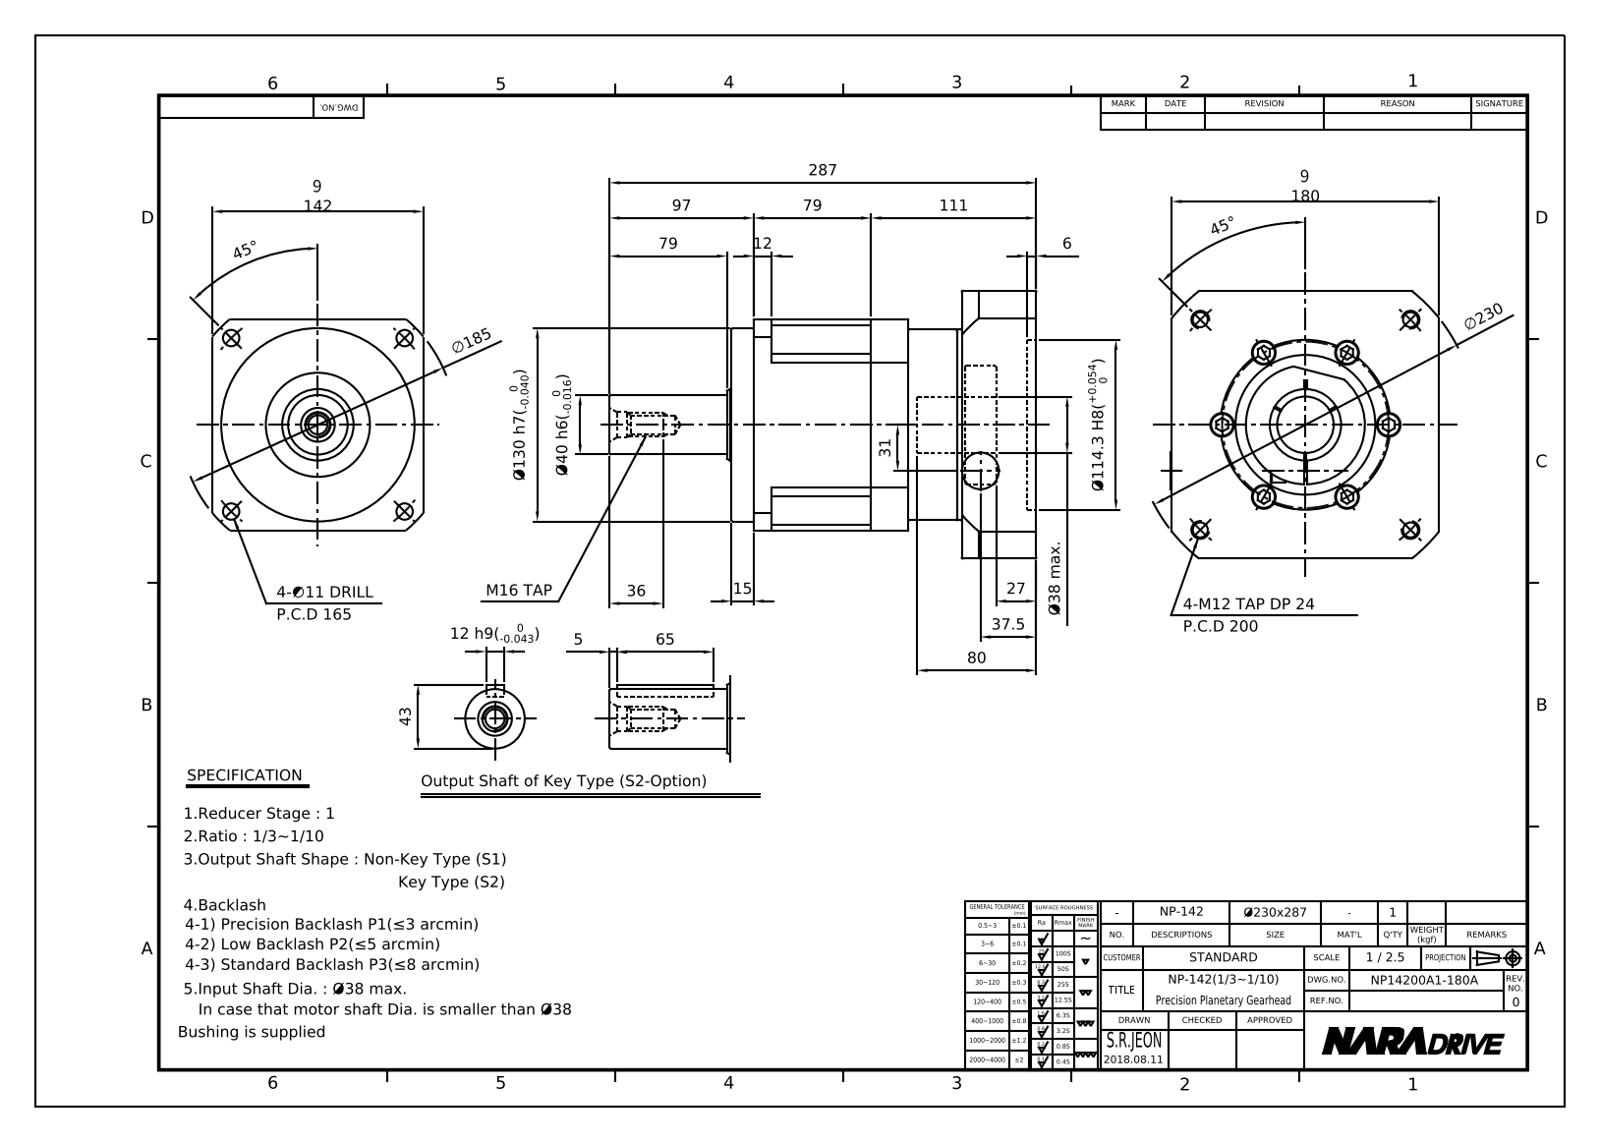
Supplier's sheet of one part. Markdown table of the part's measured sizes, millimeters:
| quantity | value |
| --- | --- |
| part name | NP14200A1-180A-S1 |
| STEP written by | Autodesk Inventor 2015 (AUTOMOTIVE_DESIGN) |
| units | millimeters |
| bodies | 2 solids, 448 faces (202 planar, 128 cylindrical, 118 other) |
| overall size | 287 × 181 × 180 |
| volume | 3 320 000 mm³ |
| surface area | 309 119 mm² |
| round holes (diameter × count) | 6.65 × 10, 14 × 10, 9 × 6, 11 × 5, 8.5 × 4, 10.11 × 4, 8.38 × 1, 12.5 × 1, 13.84 × 1, 14.5 × 1, 17 × 1, 38 × 1 |
| round bosses / shafts (diameter × count) | 13 × 11, 8 × 11, 130 × 1, 128 × 1, 80 × 1, 40 × 1, 25 × 1, 14 × 1 |
| partial cylindrical surfaces (radius × count) | 0.5 × 8, 1 × 4, 15 × 4, 9 × 1, 57.15 × 1, 82.5 × 1, 92.5 × 1, 115 × 1 |
| main face-to-face distances | 19, 161, 142, 70, 50, 120, 180, 85, 155, 205 |
| hole center spacings | 56, 97, 129.64, 35.36, 48.14, 58.39, 65.82, 72.22 |
